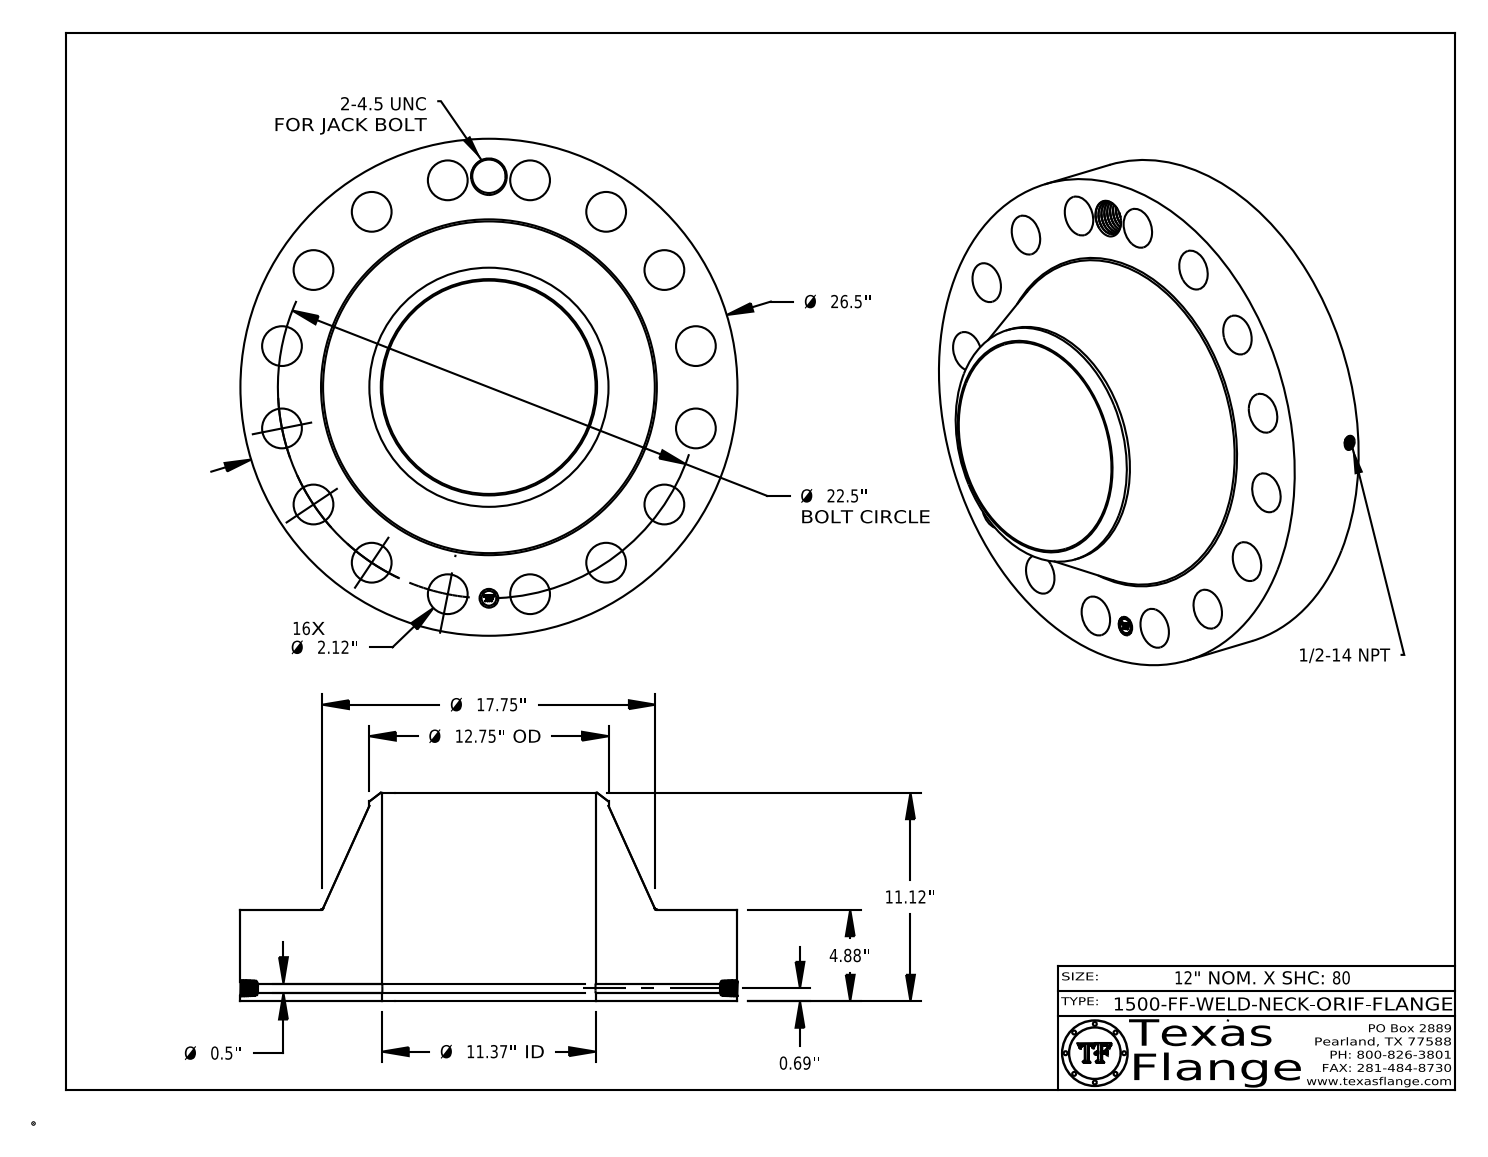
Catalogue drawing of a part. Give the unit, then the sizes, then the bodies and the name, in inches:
Units: inches
Overall size (bounding box): 26.5 × 26.5 × 11.12
Round holes (diameter × count): ⌀2.12 ×16, ⌀0.5 ×1, ⌀0.672 ×1, ⌀1 ×1, ⌀1.781 ×1, ⌀11.374 ×1
Round bosses / shafts (diameter × count): ⌀0.061 ×8, ⌀26.5 ×1, ⌀12.75 ×1, ⌀0.788 ×1
Main face-to-face distances: 4.88, 11.12, 6.24, 4.865, 0.015, 6.255, 0.298, 0.293, 0.054, 0.248
Hole centre spacings: 11.25, 8.61, 15.91, 20.787, 12.5, 18.708, 22.068, 4.389
Volume: 2 374 in³ · Surface area: 2 359 in²
Bodies: 1 solid, 824 faces (368 planar, 122 cylindrical, 334 other)
Part name (STEP PRODUCT): 1500-FF-WELD-NECK
STEP written by: CATIA V5 STEP AP214 (AUTOMOTIVE_DESIGN)
